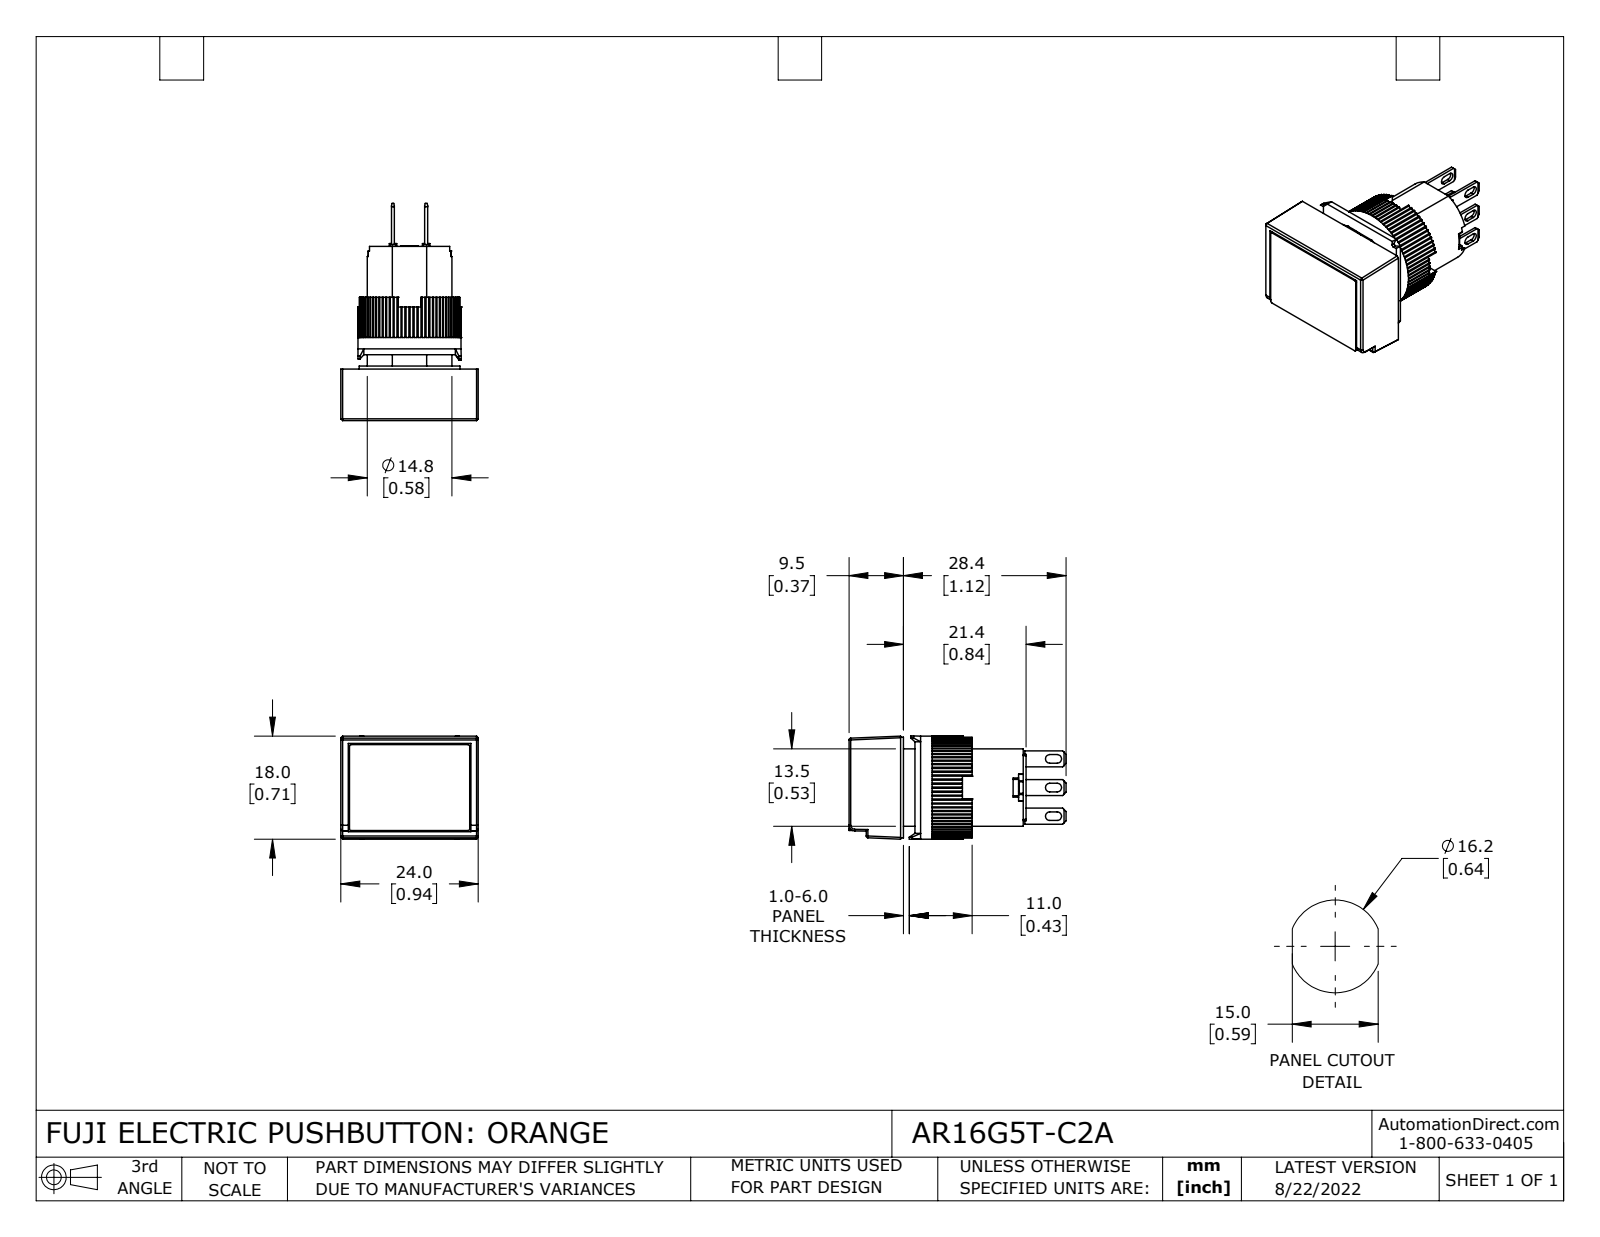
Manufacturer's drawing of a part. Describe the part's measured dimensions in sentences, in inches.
The part is named "AR16G5T-C2A". Its 3-D file was written by "SolidWorks 2021 (CONFIG_CONTROL_DESIGN)". It is 12 solids with 811 faces: 630 planar, 175 cylindrical and 6 other. Overall it measures 1.492 by 0.945 by 0.709 inches. Its volume is 0.447 cubic inches and its surface area 9.321 square inches. Round holes: 1 of diameter 0.543, 1 of diameter 0.583. Round bosses or shafts: 1 of diameter 0.709, 1 of diameter 0.693. Partial cylindrical surfaces (rounded edges, fillets, slot ends): 80 of radius 0.01, 12 of radius 0.008, 6 of radius 0.012, 6 of radius 0.03, 1 of radius 0.039. The main face-to-face distances are 0.213, 0.354, 0.142, 0.492, 0.35, 0.138, 0.02, 0.843, 0.059, 0.453.
